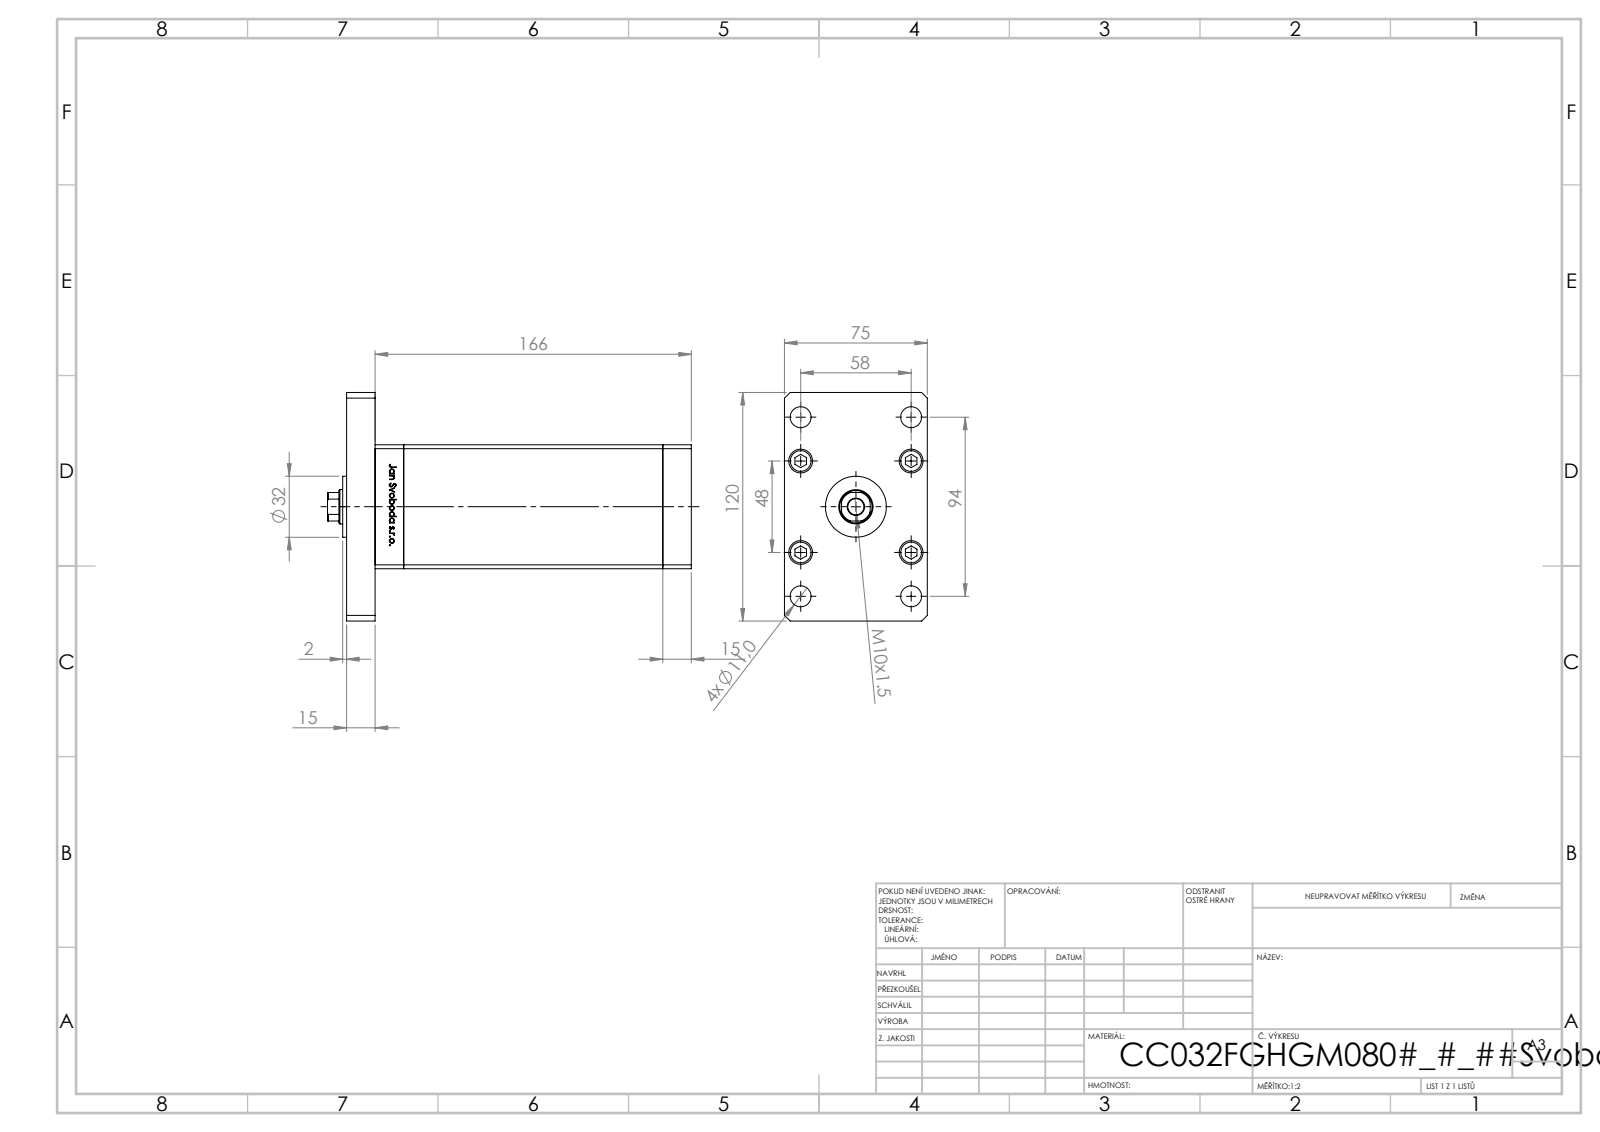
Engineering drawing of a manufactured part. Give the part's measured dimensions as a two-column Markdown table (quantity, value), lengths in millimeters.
| quantity | value |
| --- | --- |
| part name | V220C_F_MIDDLE; V220C BACK_F; ALLEN BOLT; V220C_VC_F (+2 more) |
| STEP written by | SolidWorks 2019 (CONFIG_CONTROL_DESIGN) |
| units | millimeters |
| bodies | 19 solids, 1308 faces (515 planar, 187 cylindrical, 606 other) |
| overall size | 191 × 120 × 75 |
| volume | 848 554 mm³ |
| surface area | 159 946 mm² |
| round holes (diameter × count) | 9 × 5, 13.5 × 5, 8 × 4, 11 × 4, 12.5 × 4, 2 × 2, 13.16 × 2, 8.5 × 1, 18 × 1, 19.5 × 1 |
| round bosses / shafts (diameter × count) | 12.5 × 5, 8 × 5, 32 × 1 |
| partial cylindrical surfaces (radius × count) | 0.93 × 2, 8.5 × 1 |
| main face-to-face distances | 15, 75, 151, 166, 65, 30, 136, 181, 13, 153 |
| hole center spacings | 24, 23, 37.64, 55.23, 58, 62.39, 71, 91.68 |
